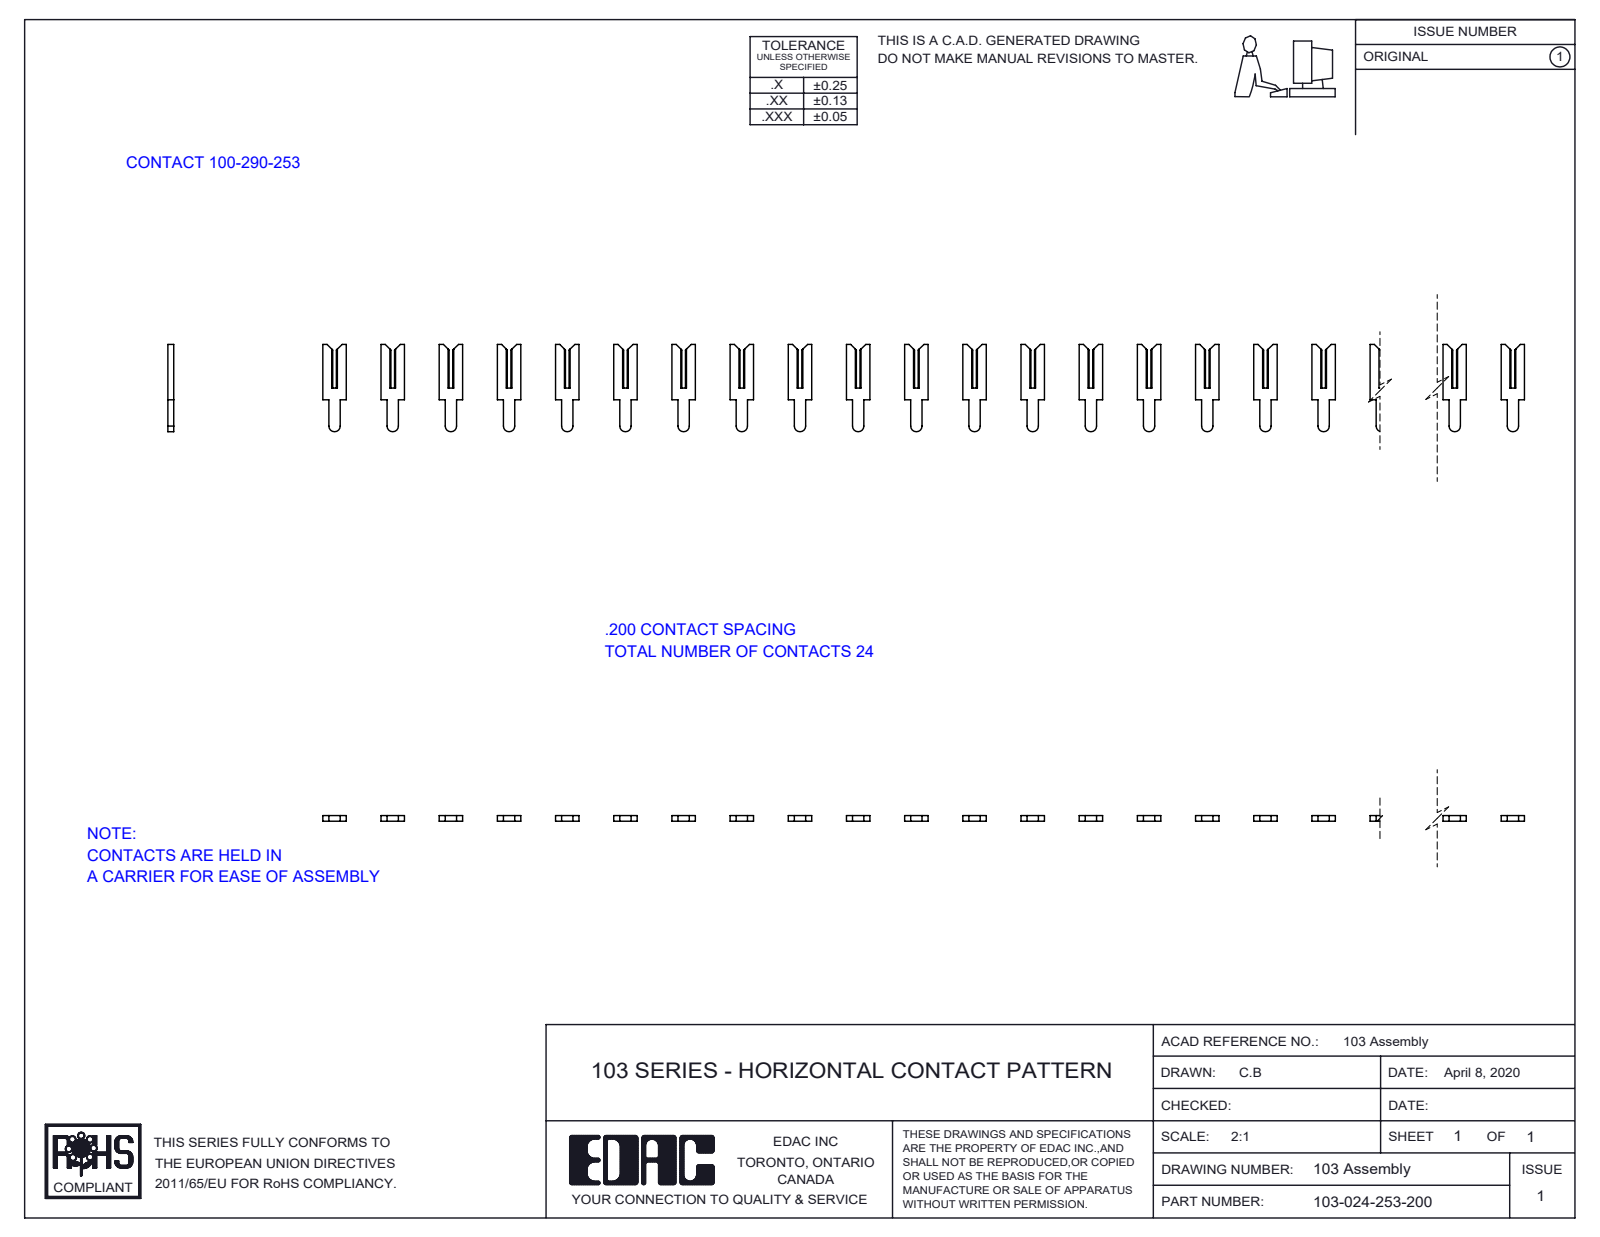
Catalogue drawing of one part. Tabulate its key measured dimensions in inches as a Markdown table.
| quantity | value |
| --- | --- |
| part name | 103-024-253-200; 100-290-001_100-290-253 |
| STEP written by | SolidWorks 2016 (CONFIG_CONTROL_DESIGN) |
| units | inches |
| bodies | 24 solids, 480 faces (456 planar, 24 cylindrical, 0 other) |
| overall size | 4.68 × 0.3 × 0.02 |
| volume | 0.008 in³ |
| surface area | 1.28 in² |
| partial cylindrical surfaces (radius × count) | 0.019 × 24 |
| main face-to-face distances | 0.02, 0.2, 0.4, 0.141, 0.6, 0.848, 0.283, 0.8, 0.99, 0.707 |
